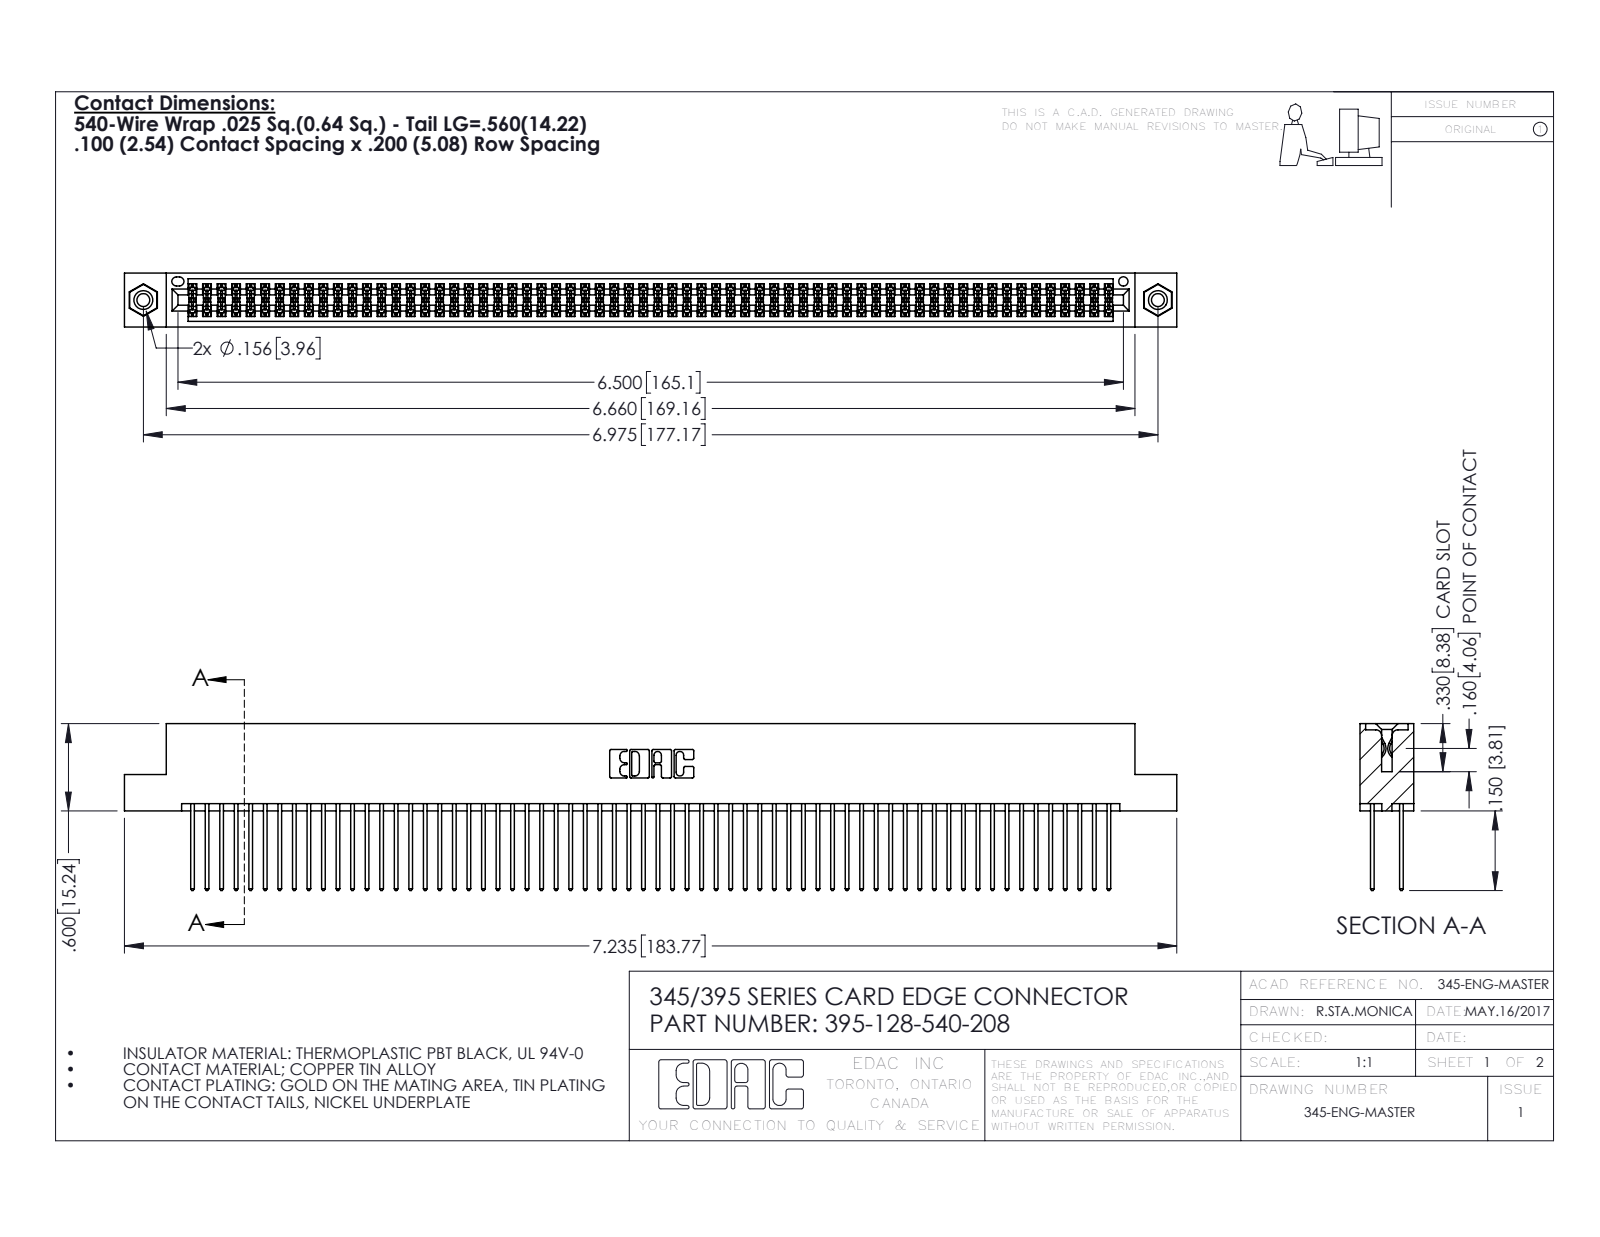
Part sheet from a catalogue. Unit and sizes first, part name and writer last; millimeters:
Units: millimetres
Overall size (bounding box): 183.8 × 29.1 × 9.4
Round holes (diameter × count): ⌀2.3 ×2, ⌀3.2 ×2, ⌀4 ×2, ⌀1.6 ×1
Round bosses / shafts (diameter × count): ⌀3.9 ×2
Partial cylindrical surfaces — rounded edges, fillets, slot ends (radius × count): R0.2 ×192, R0.3 ×128, R0.3 ×22, R0.2 ×6, R0.8 ×6, R0.7 ×3, R0.4 ×2, R0.5 ×2
Main face-to-face distances: 1.8, 7.6, 5.1, 2.5, 6.9, 0.6, 9.4, 5.7, 4.4, 3.8
Hole centre spacings: 6.9, 171.2, 177.2
Volume: 18 530 mm³ · Surface area: 30 090 mm²
Bodies: 131 solids, 6586 faces (4336 planar, 2234 cylindrical, 16 other)
Part name (STEP PRODUCT): 345 Part_Flush Mounting Lugs - 0.156 Dia-TI; 395-128-540-208; 345-292-001_345-293-140; 345-250-001_345-250-003-102
STEP written by: SolidWorks 2016 (CONFIG_CONTROL_DESIGN)
